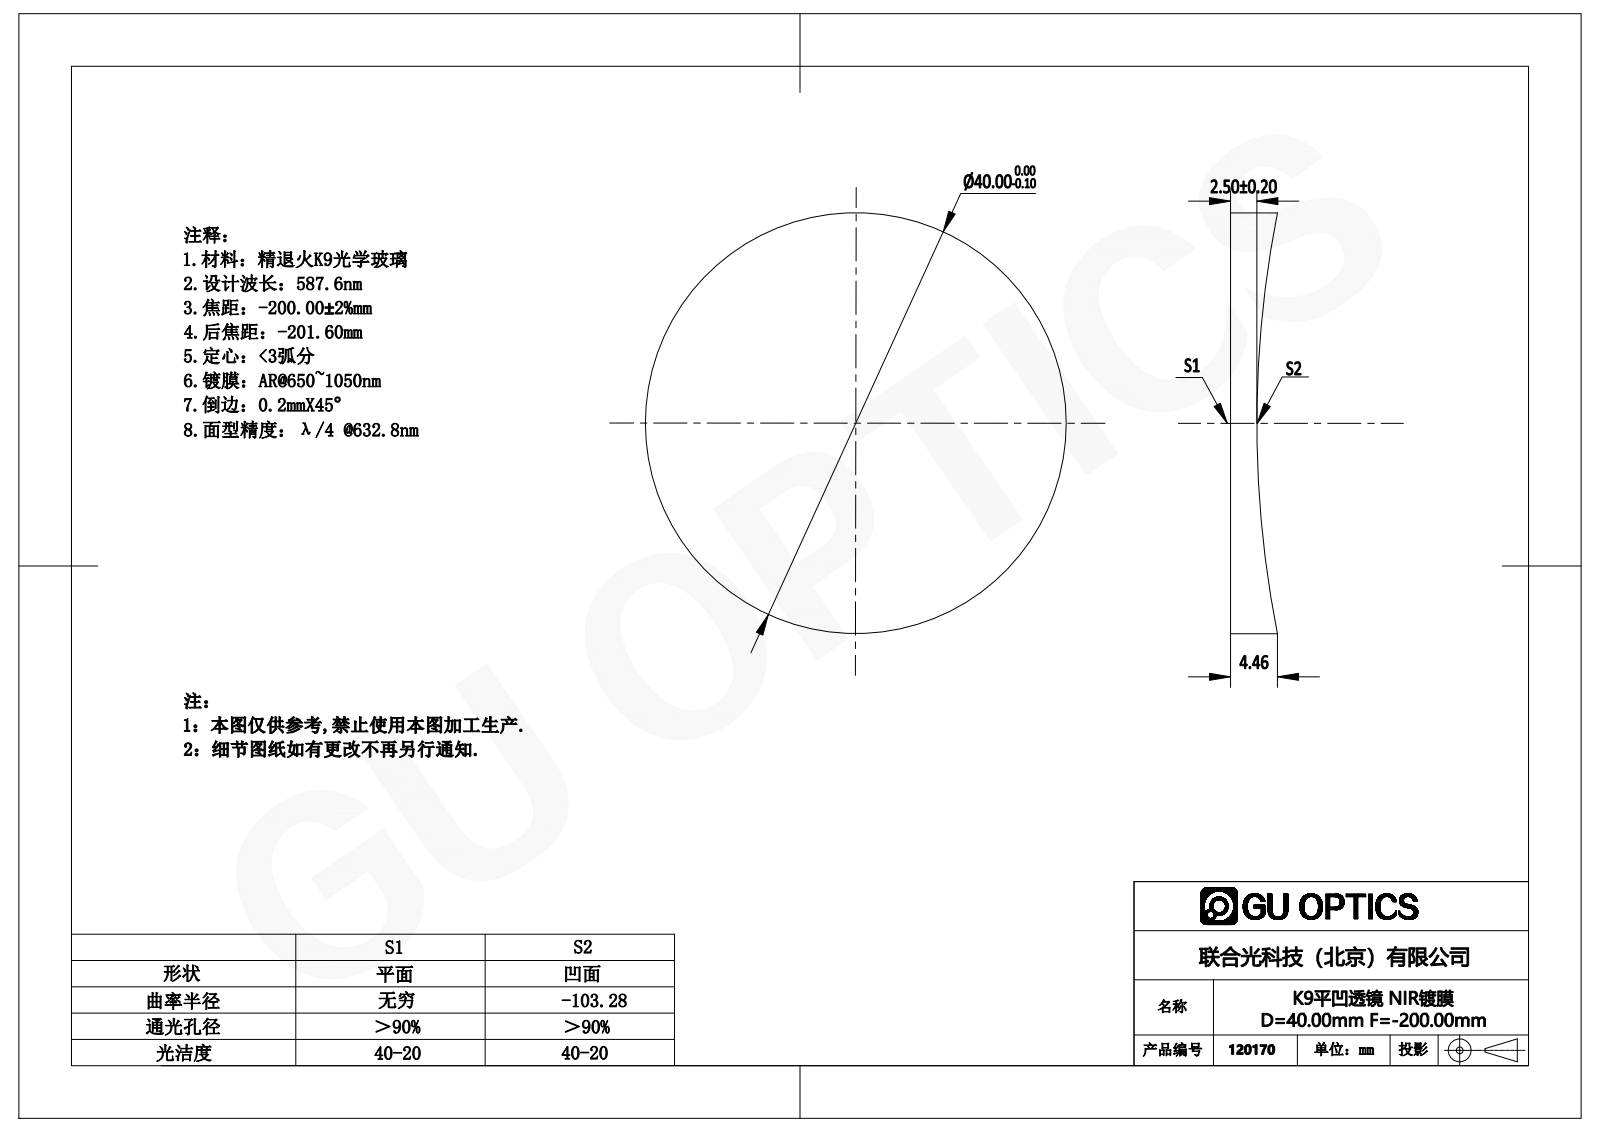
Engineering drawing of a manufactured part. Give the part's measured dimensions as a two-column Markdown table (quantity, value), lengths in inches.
| quantity | value |
| --- | --- |
| part name | 120170 |
| STEP written by | SolidWorks 2016 (AUTOMOTIVE_DESIGN) |
| units | inches |
| bodies | 1 solid, 5 faces (1 planar, 2 cylindrical, 2 other) |
| overall size | 1.575 × 1.575 × 0.176 |
| volume | 0.266 in³ |
| surface area | 4.782 in² |
| round bosses / shafts (diameter × count) | 1.575 × 1 |
